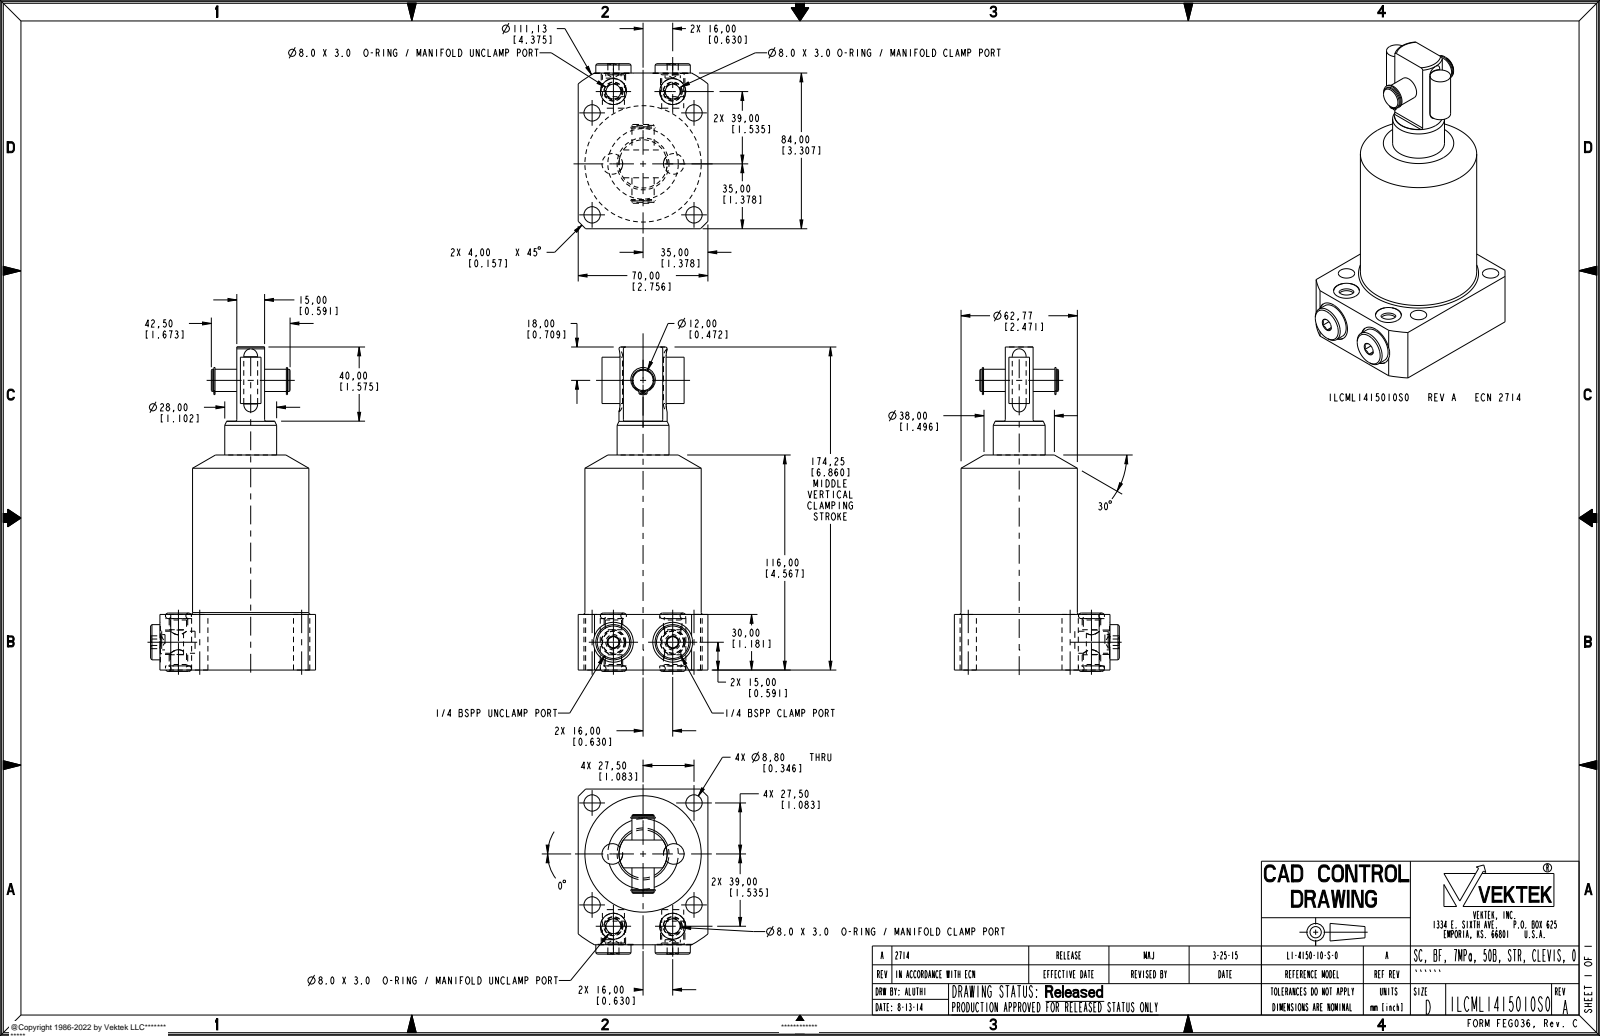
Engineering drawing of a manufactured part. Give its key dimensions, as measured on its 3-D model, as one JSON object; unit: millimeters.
{"part_name": "ILCML1415010S0", "step_written_by": "PRO/ENGINEER BY PARAMETRIC TECHNOLOGY CORPORATION, 2013320 (CONFIG_CONTROL_DESIGN)", "units": "millimeters", "bodies": {"solids": 7, "faces": 240, "planar": 80, "cylindrical": 96, "other": 64}, "overall_size": [166, 89.05, 70], "volume_mm3": 449711, "surface_area_mm2": 52993, "round_holes": [[8.8, 4], [1.04, 2], [8.75, 2], [11.89, 2], [14, 2], [21.5, 2]], "round_bosses_or_shafts": [[19, 2], [13.16, 2], [11.12, 2], [10, 2], [8.25, 2], [62.77, 1], [28, 1], [26, 1]], "partial_cylinders_radius": [[0.8, 2], [1.04, 2], [1.09, 2], [5.56, 2], [55.56, 1]], "face_to_face_distances": [70, 30, 84, 42.5, 27.5, 15, 41.5, 56.5, 116, 86], "hole_center_spacings": [55, 16.26, 32, 44.99, 67.49, 77.78, 79.46, 126.49]}
